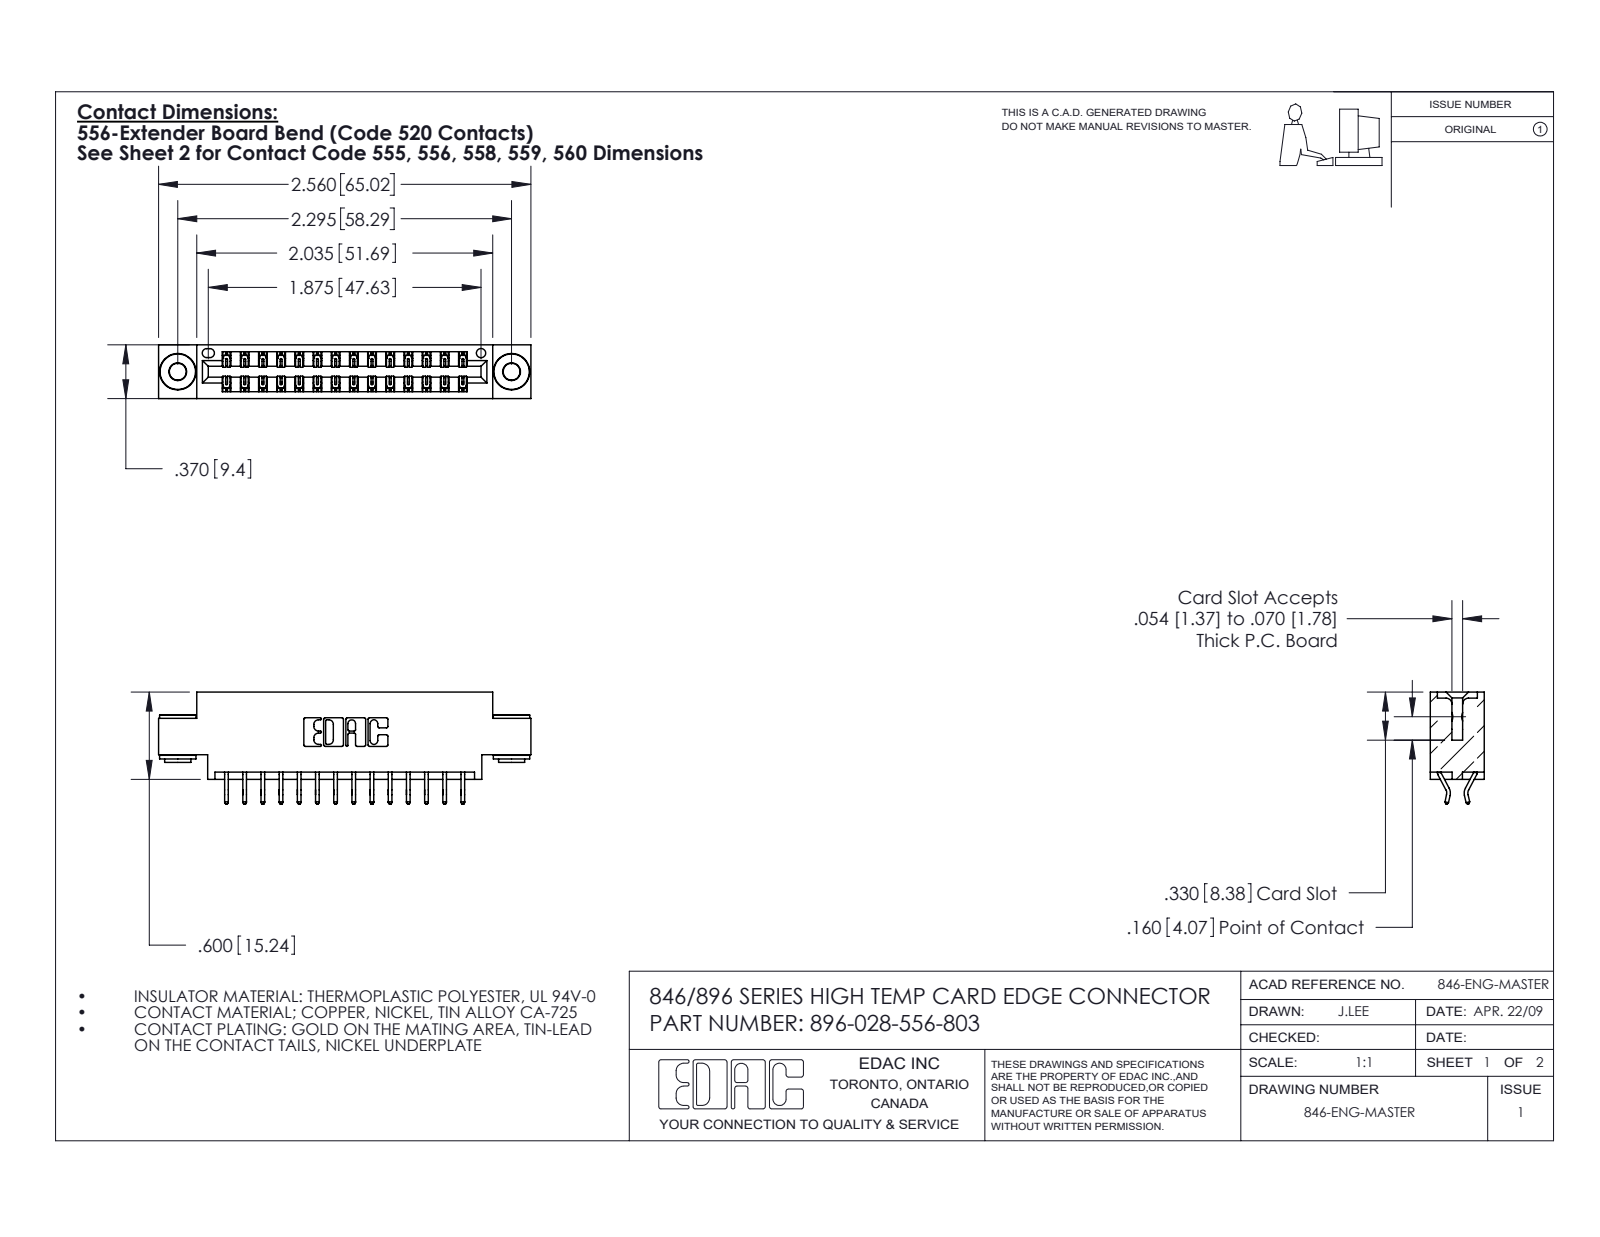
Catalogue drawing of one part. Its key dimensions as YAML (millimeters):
part_name: "396-028-556-803; 345-250-002_345-250-002-102; 345-292-001_556 Tail; 346 Part_0.170 Offset - 0.156 Dia-TH"
step_written_by: "SolidWorks 2016 (CONFIG_CONTROL_DESIGN)"
units: millimeters
bodies: {solids: 31, faces: 1788, planar: 1182, cylindrical: 598, other: 8}
overall_size: [65, 19.6, 9.4]
volume: 5980
surface_area: 8155
round_holes:
  - {diameter: 2.9, count: 2}
  - {diameter: 4, count: 2}
  - {diameter: 1.6, count: 1}
round_bosses_or_shafts:
  - {diameter: 6.4, count: 2}
  - {diameter: 4.6, count: 2}
  - {diameter: 3.5, count: 2}
partial_cylinders:
  - {radius: 0.2, count: 42}
  - {radius: 0.3, count: 22}
  - {radius: 0.2, count: 6}
  - {radius: 0.8, count: 6}
  - {radius: 0.7, count: 3}
  - {radius: 0.3, count: 2}
  - {radius: 0.4, count: 2}
  - {radius: 0.6, count: 2}
face_to_face_distances: [9.4, 1.2, 8.2, 6.4, 0.6, 7, 1.8, 7.6, 3.8, 5.6]
hole_center_spacings: [6.2, 53.1, 58.3]
